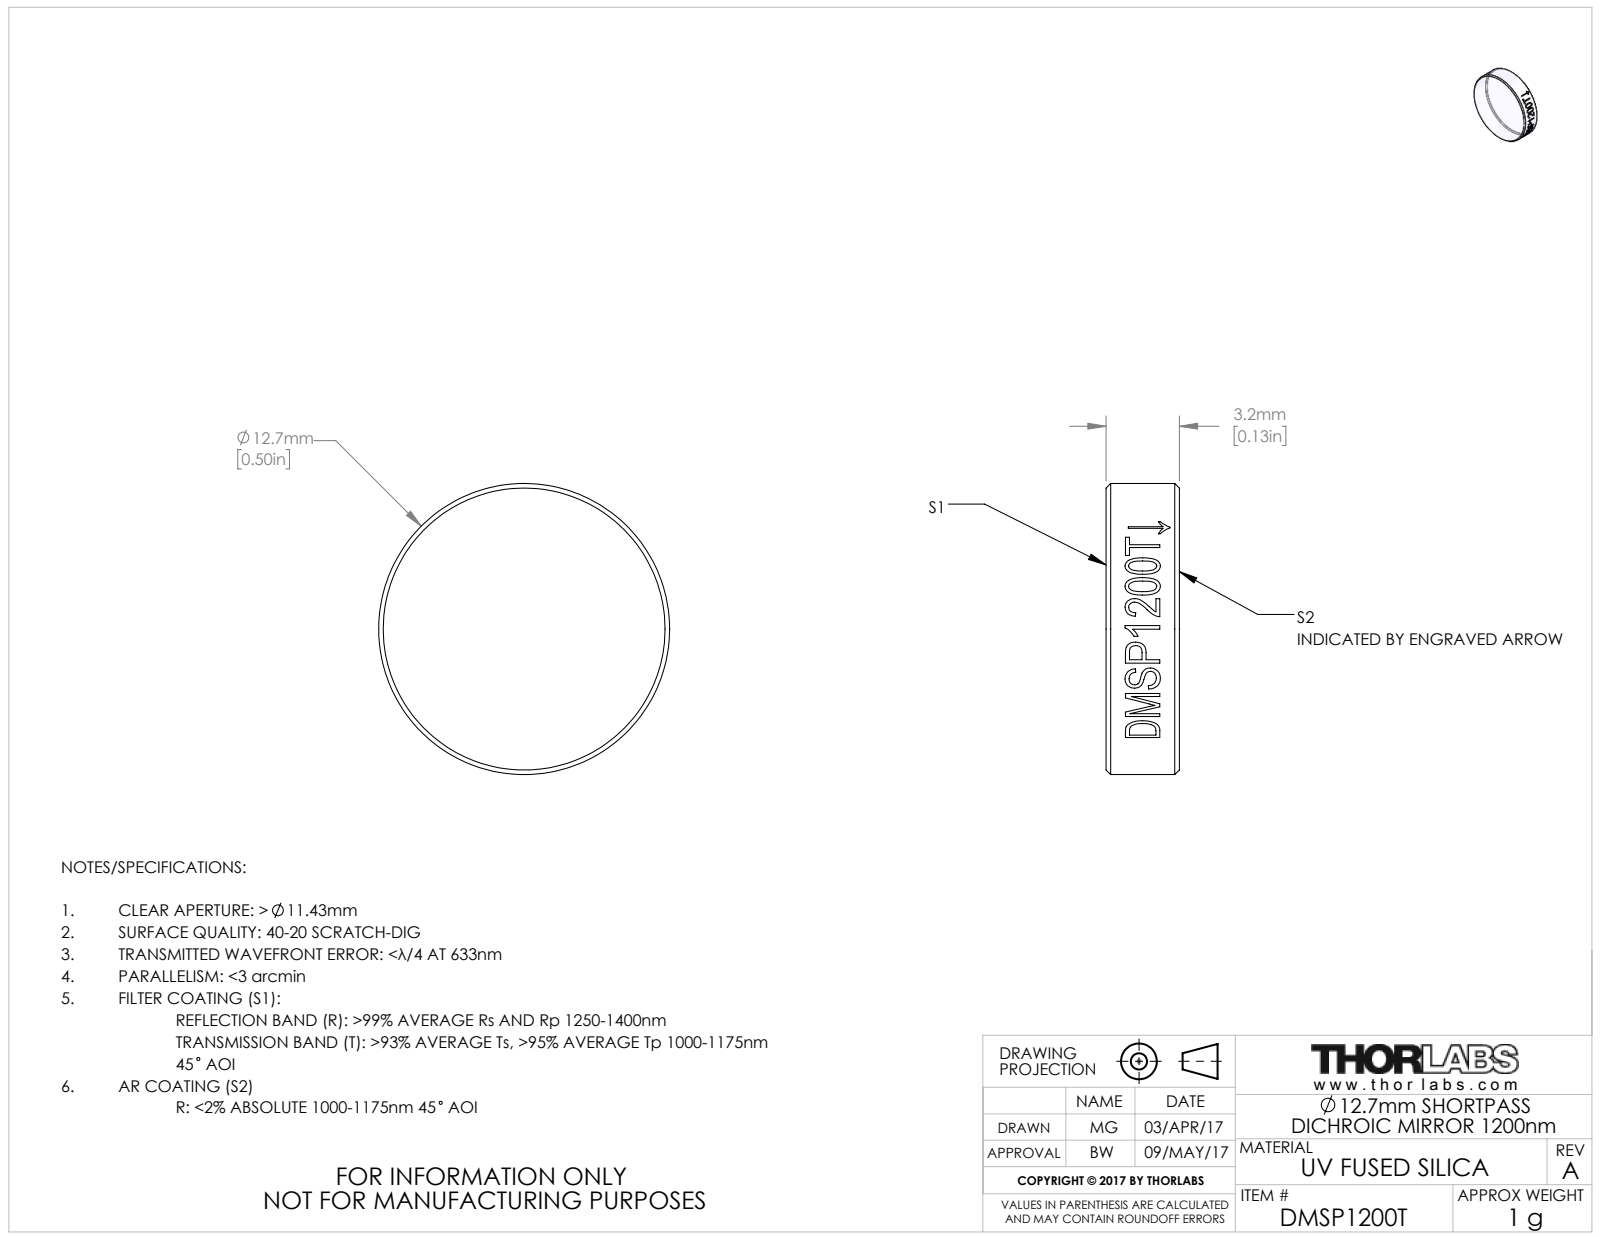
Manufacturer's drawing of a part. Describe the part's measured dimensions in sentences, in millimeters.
The part is named "TTN128495-E0W". Its 3-D file was written by "SolidWorks 2016 (CONFIG_CONTROL_DESIGN)". It is 1 solid with 22 faces: 2 planar, 16 cylindrical and 4 other. Overall it measures 12.7 by 12.7 by 3.2 millimeters. Its volume is 410 cubic millimeters and its surface area 372 square millimeters. Round bosses or shafts: 1 of diameter 12.7. The main face-to-face distances are 3.2.
